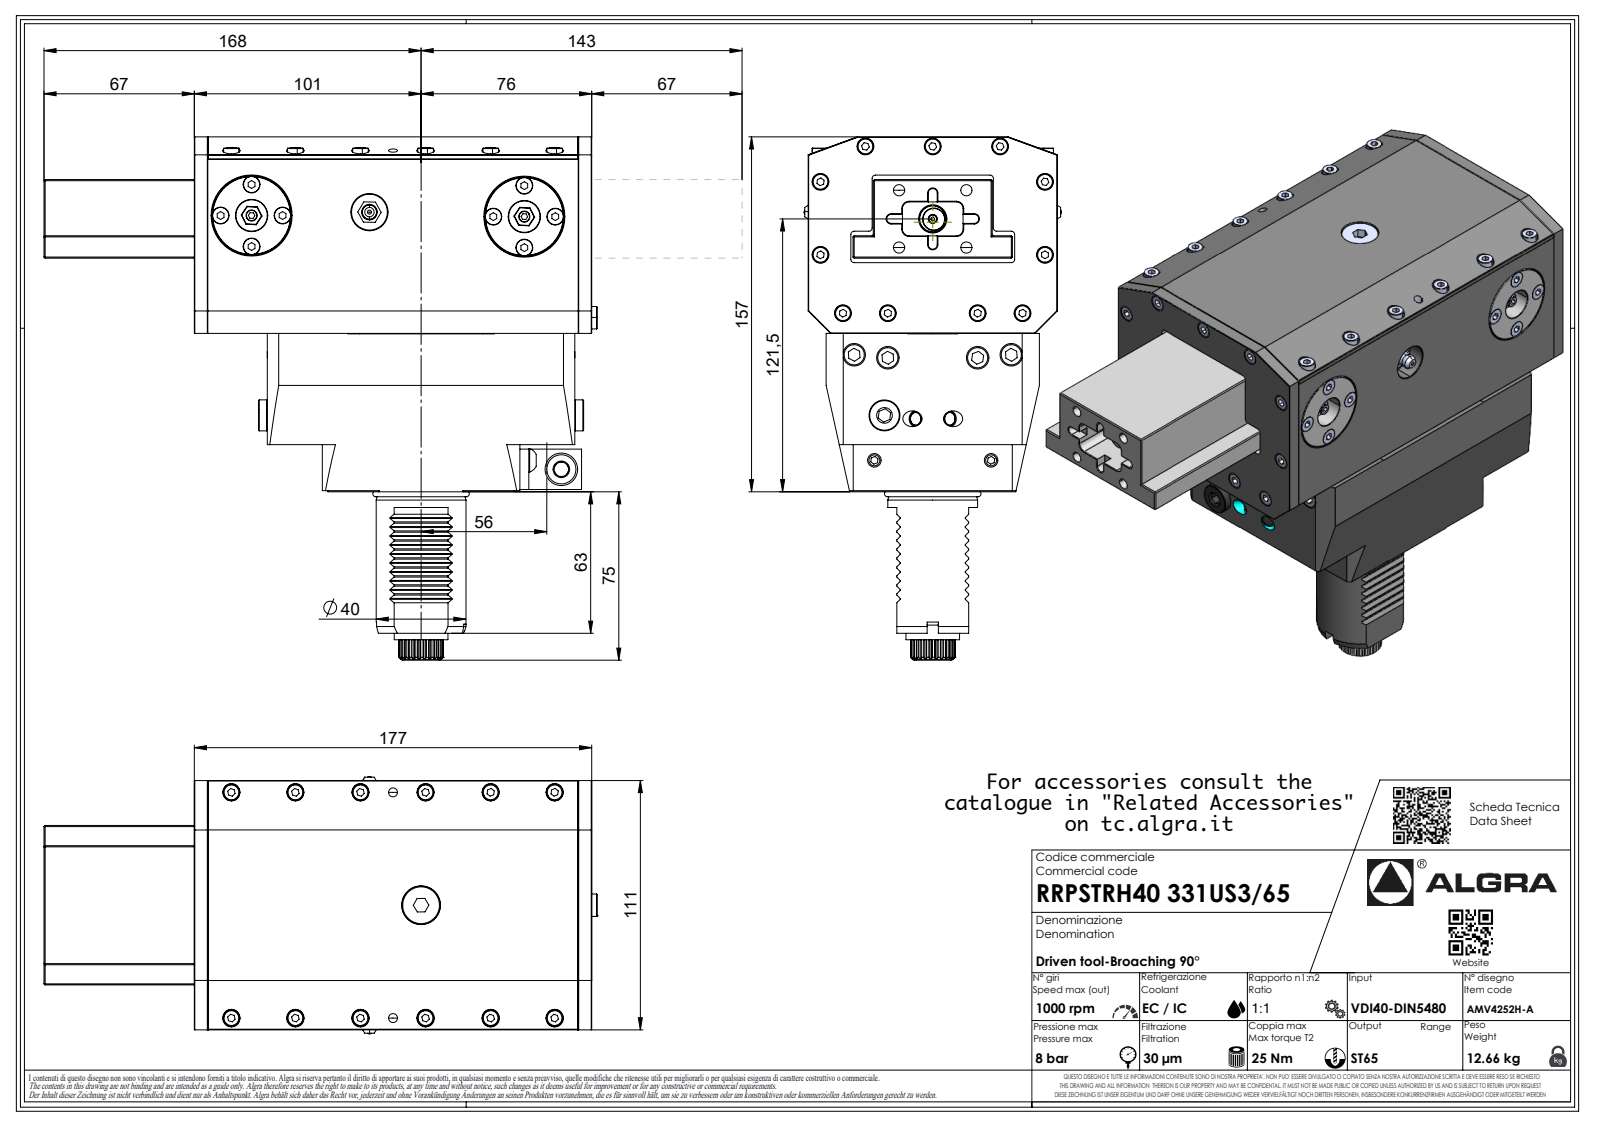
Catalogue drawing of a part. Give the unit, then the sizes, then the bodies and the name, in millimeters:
Units: millimetres
Overall size (bounding box): 246.47 × 233 × 114.6
Round holes (diameter × count): ⌀2.1 ×1, ⌀26 ×1, ⌀61 ×1
Round bosses / shafts (diameter × count): ⌀55 ×1, ⌀40 ×1, ⌀38.7 ×1, ⌀23.9 ×1, ⌀10 ×1, ⌀6.37 ×1, ⌀1.7 ×1
Partial cylindrical surfaces — rounded edges, fillets, slot ends (radius × count): R0.3 ×20, R3.5 ×12, R0.33 ×7, R0.52 ×7, R3.7 ×7, R3 ×4, R0.21 ×1, R2.5 ×1
Main face-to-face distances: 111, 137, 177, 103, 21, 87.5, 8, 83, 139, 33.5
Volume: 2 666 000 mm³ · Surface area: 146 645 mm²
Bodies: 1 solid, 912 faces (582 planar, 132 cylindrical, 198 other)
Part name (STEP PRODUCT): RRPSTRH40331US365
STEP written by: SolidWorks 2023 (AUTOMOTIVE_DESIGN)
